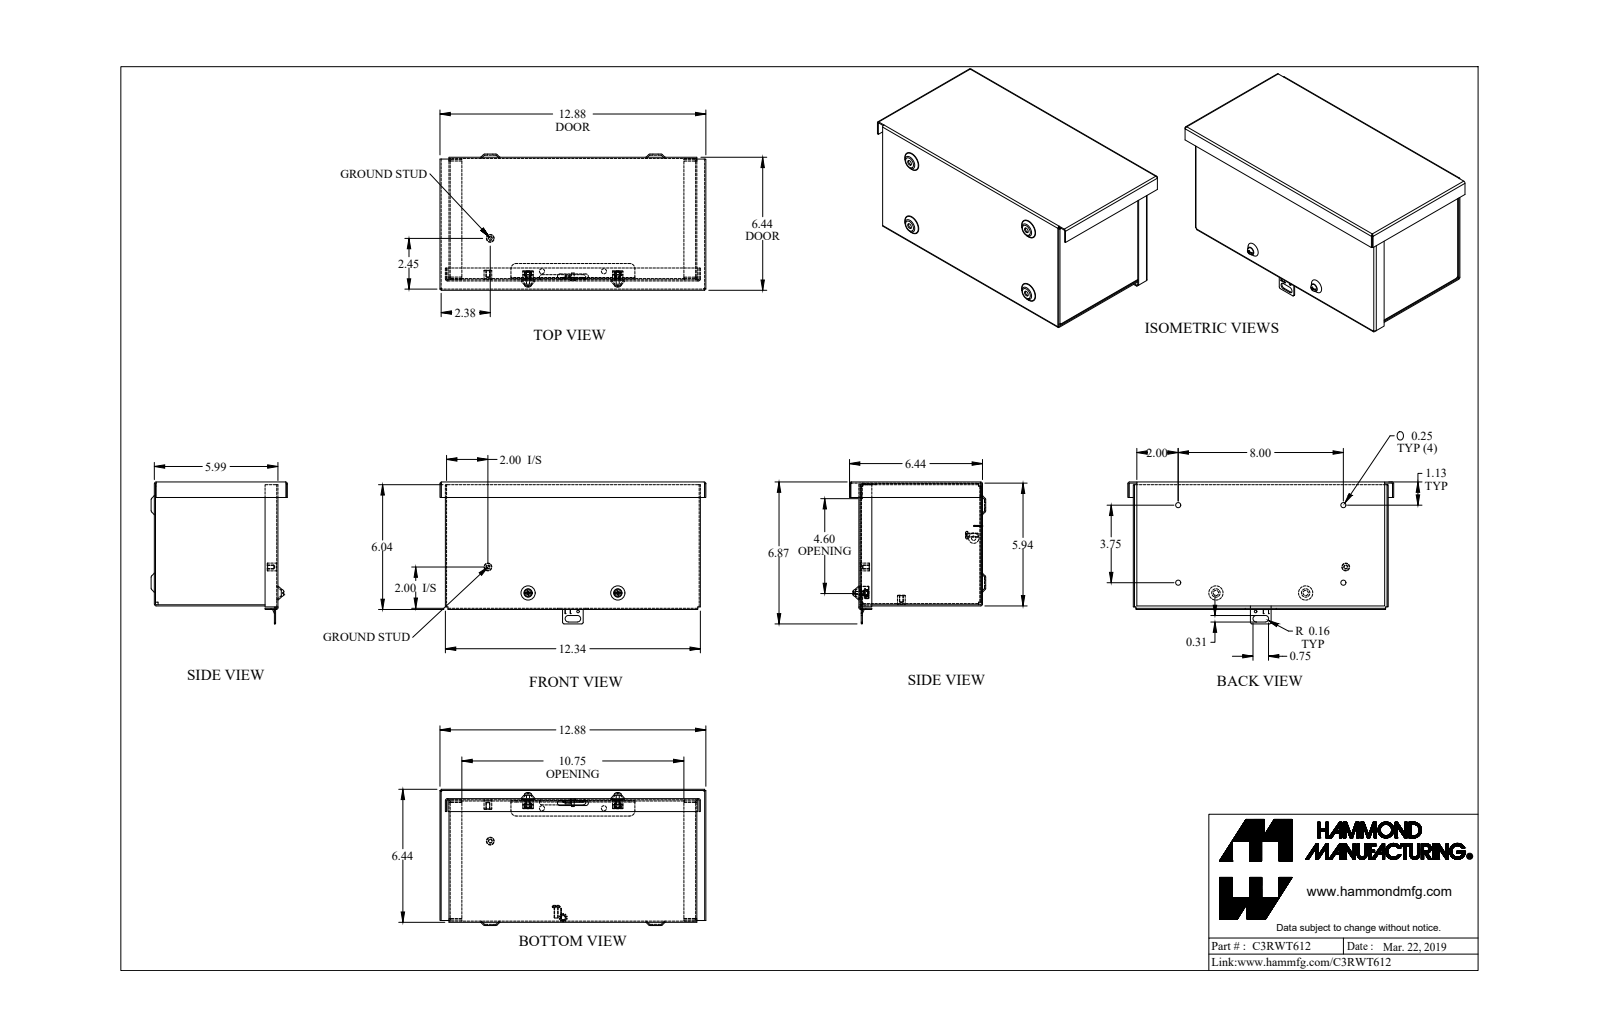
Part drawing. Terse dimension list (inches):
name: C3RWT612_Default
written by: SolidWorks 2019 (CONFIG_CONTROL_DESIGN)
unit: in
bodies: 19 solids, 645 faces (344 planar, 201 cylindrical, 100 other)
size: 13.5 × 6.871 × 6.594
volume: 25.63 in³; area: 906.4 in²
holes: 6× ⌀0.25, 4× ⌀0.156, 2× ⌀0.203, 2× ⌀0.214, 2× ⌀0.23, 1× ⌀0.125, 1× ⌀0.137, 1× ⌀0.2, 1× ⌀0.215
bosses: 3× ⌀0.19, 2× ⌀0.375, 2× ⌀0.148, 1× ⌀0.5, 1× ⌀0.367, 1× ⌀0.21, 1× ⌀0.152, 1× ⌀0.125
rounds: 18× R0.029, 18× R0.086, 12× R0.125, 8× R0.08, 8× R0.108, 6× R0.25, 4× R0.016, 4× R0.022
face distances: 0.057, 5.943, 5.928, 5.871, 5.886, 6, 5.985, 11.943, 12, 11.886
hole spacings: 3.15, 10.697, 1.895, 2.179, 3.75, 4.057, 4.626, 4.964
